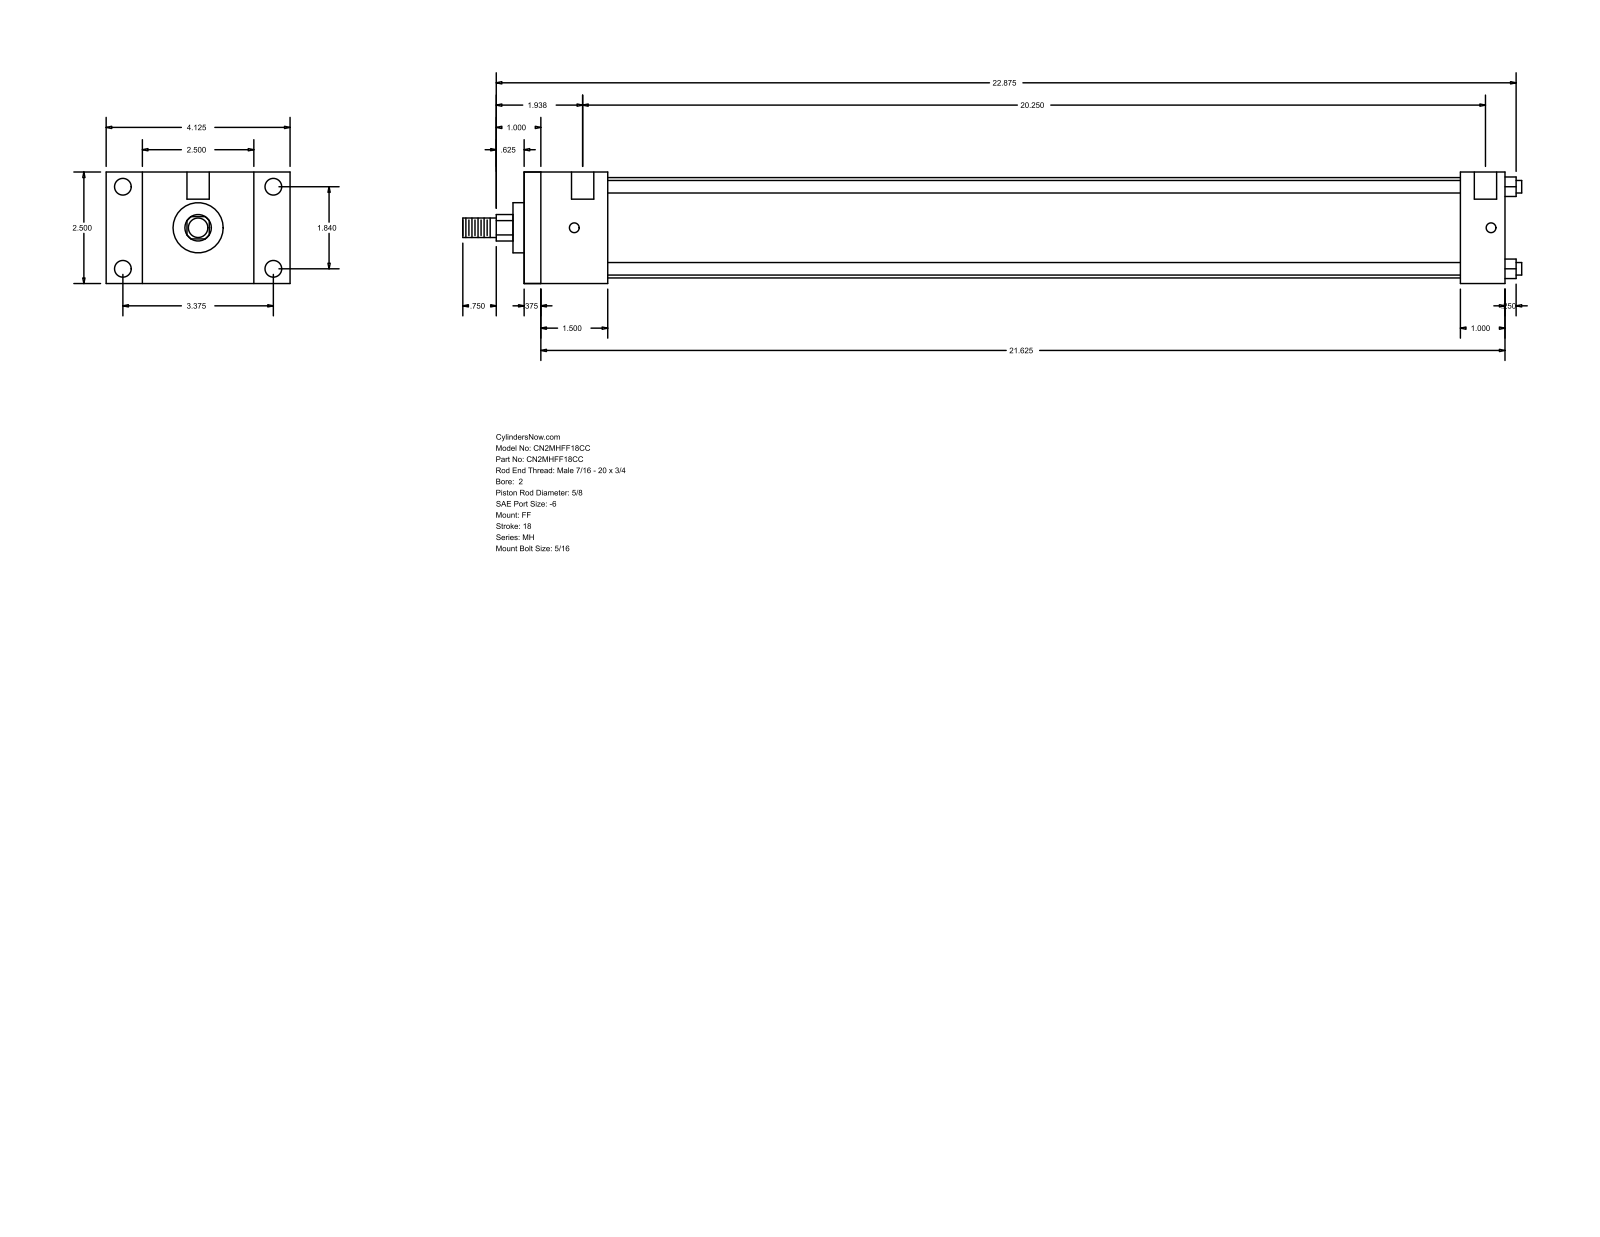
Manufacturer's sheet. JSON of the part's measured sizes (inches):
{"part_name": "MH_FF__0200_0.625", "step_written_by": "GSSL Pune (CONFIG_CONTROL_DESIGN)", "units": "inches", "bodies": {"solids": 0, "faces": 92, "planar": 64, "cylindrical": 28, "other": 0}, "overall_size": [23.75, 4.125, 2.5], "round_holes": [[0.219, 4], [0.375, 4], [0.5, 2]], "round_bosses_or_shafts": [[0.281, 4], [2.25, 1], [1.125, 1], [0.625, 1], [0.437, 1]], "partial_cylinders_radius": [[0.297, 1]], "face_to_face_distances": [2.5, 22, 21.625, 0.375, 1, 1.5, 1.875, 21, 20.625, 19.125], "hole_center_spacings": [1.84, 3.375, 3.844, 20.563, 0.125, 0.187, 20.25, 20.375]}
